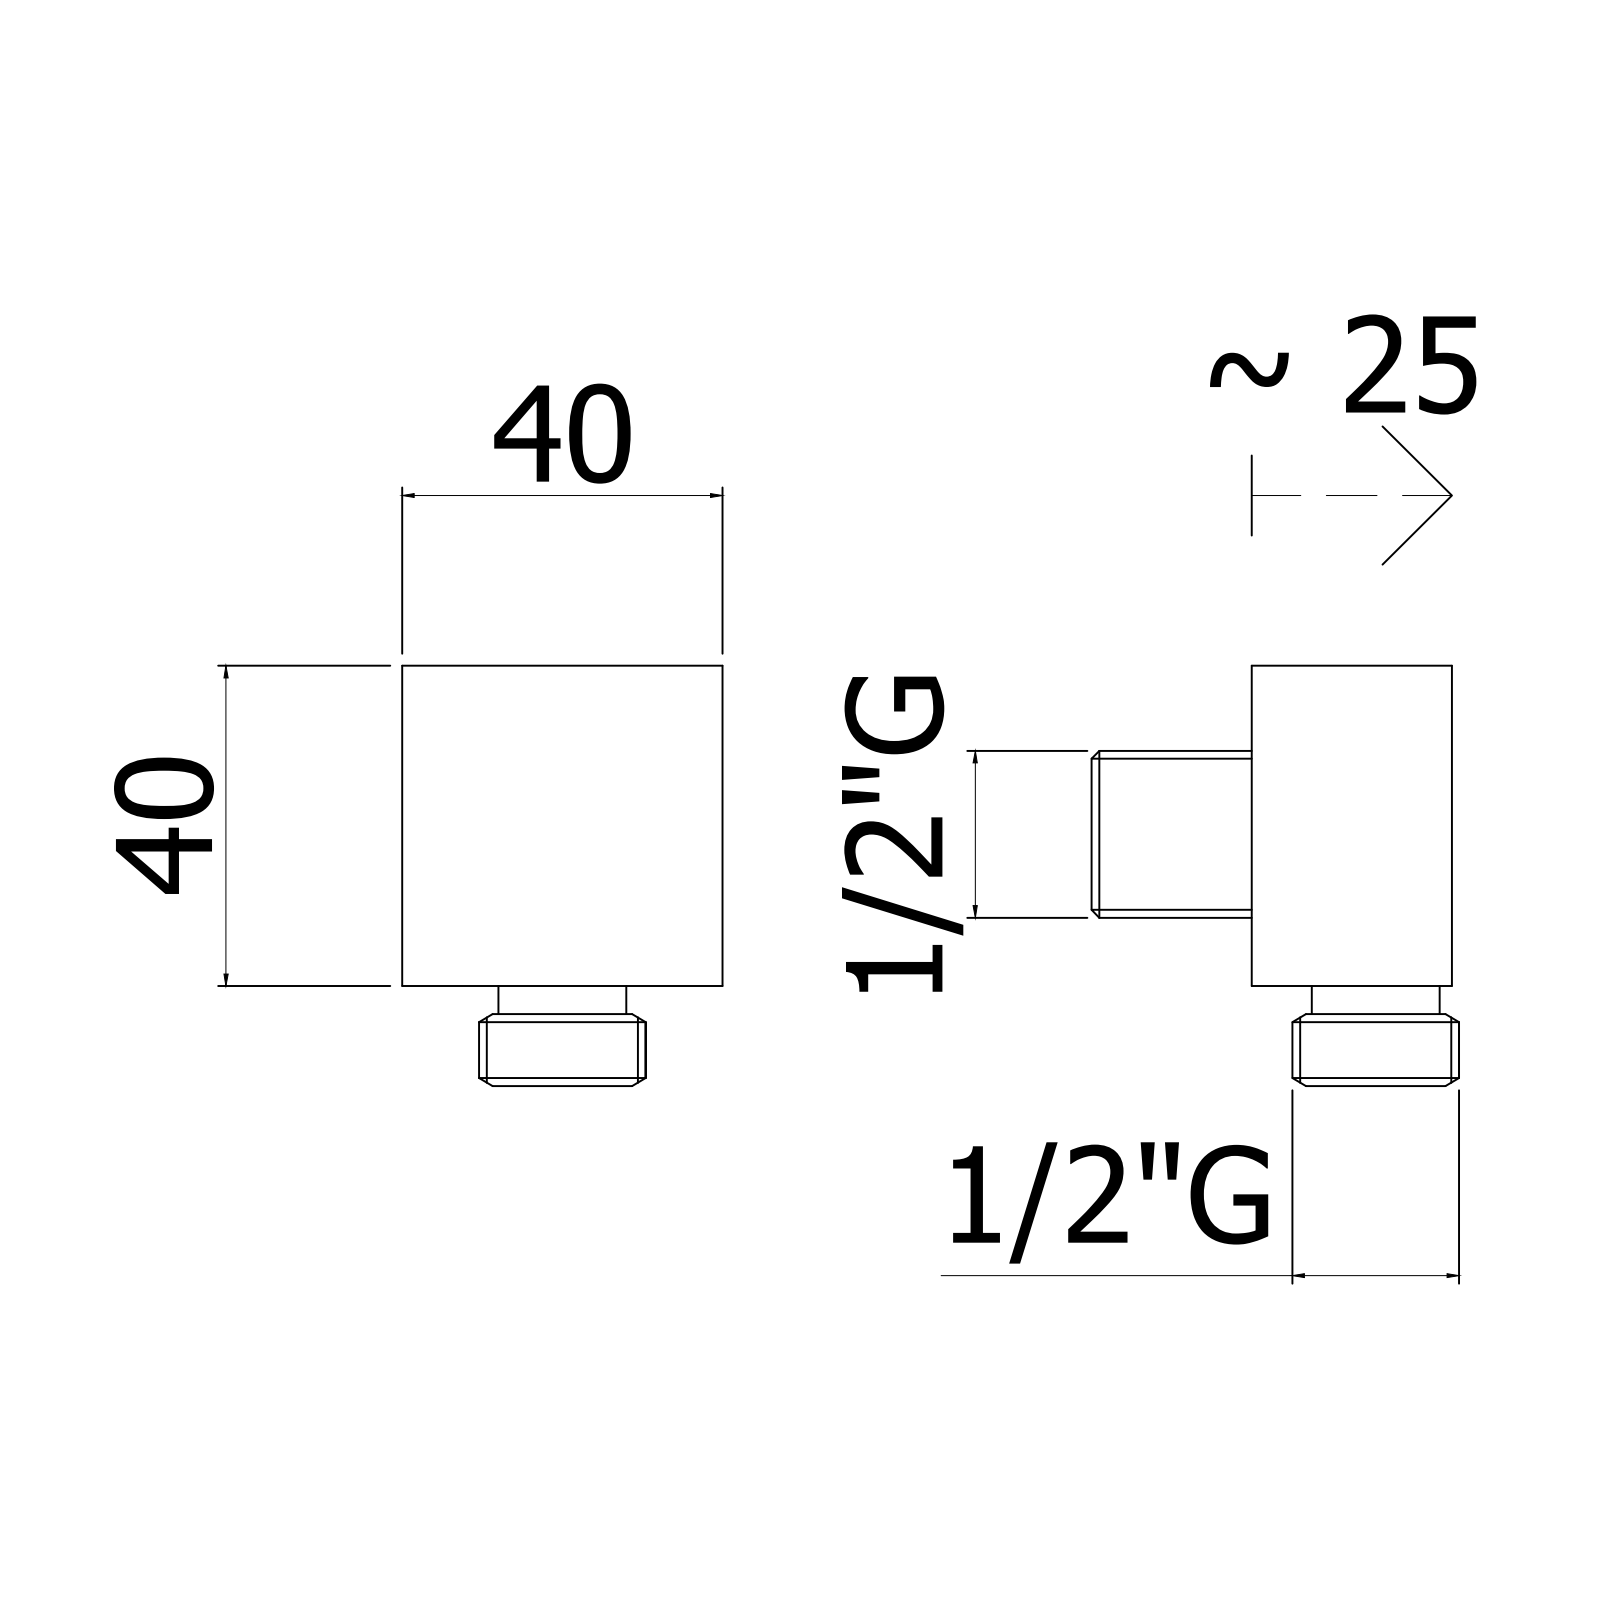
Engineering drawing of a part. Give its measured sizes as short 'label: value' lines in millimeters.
name: 4071742CR
written by: CREO PARAMETRIC BY PTC INC, 2020044 (CONFIG_CONTROL_DESIGN)
unit: mm
bodies: 1 solid, 339 faces (68 planar, 161 cylindrical, 110 other)
size: 59.6 × 42.5 × 40
volume: 2 732 mm³; area: 17 820 mm²
holes: 1× ⌀8, 1× ⌀10.5, 1× ⌀11.04, 1× ⌀12.15, 1× ⌀14.5, 1× ⌀15, 1× ⌀16.5, 1× ⌀18.9, 1× ⌀20.95
bosses: 2× ⌀18.63, 1× ⌀18.6, 1× ⌀16, 1× ⌀11.88, 1× ⌀10.74
rounds: 12× R0.2
face distances: 40, 25, 2.2, 22.8, 12.5, 5, 10.3, 1, 39, 14.1
